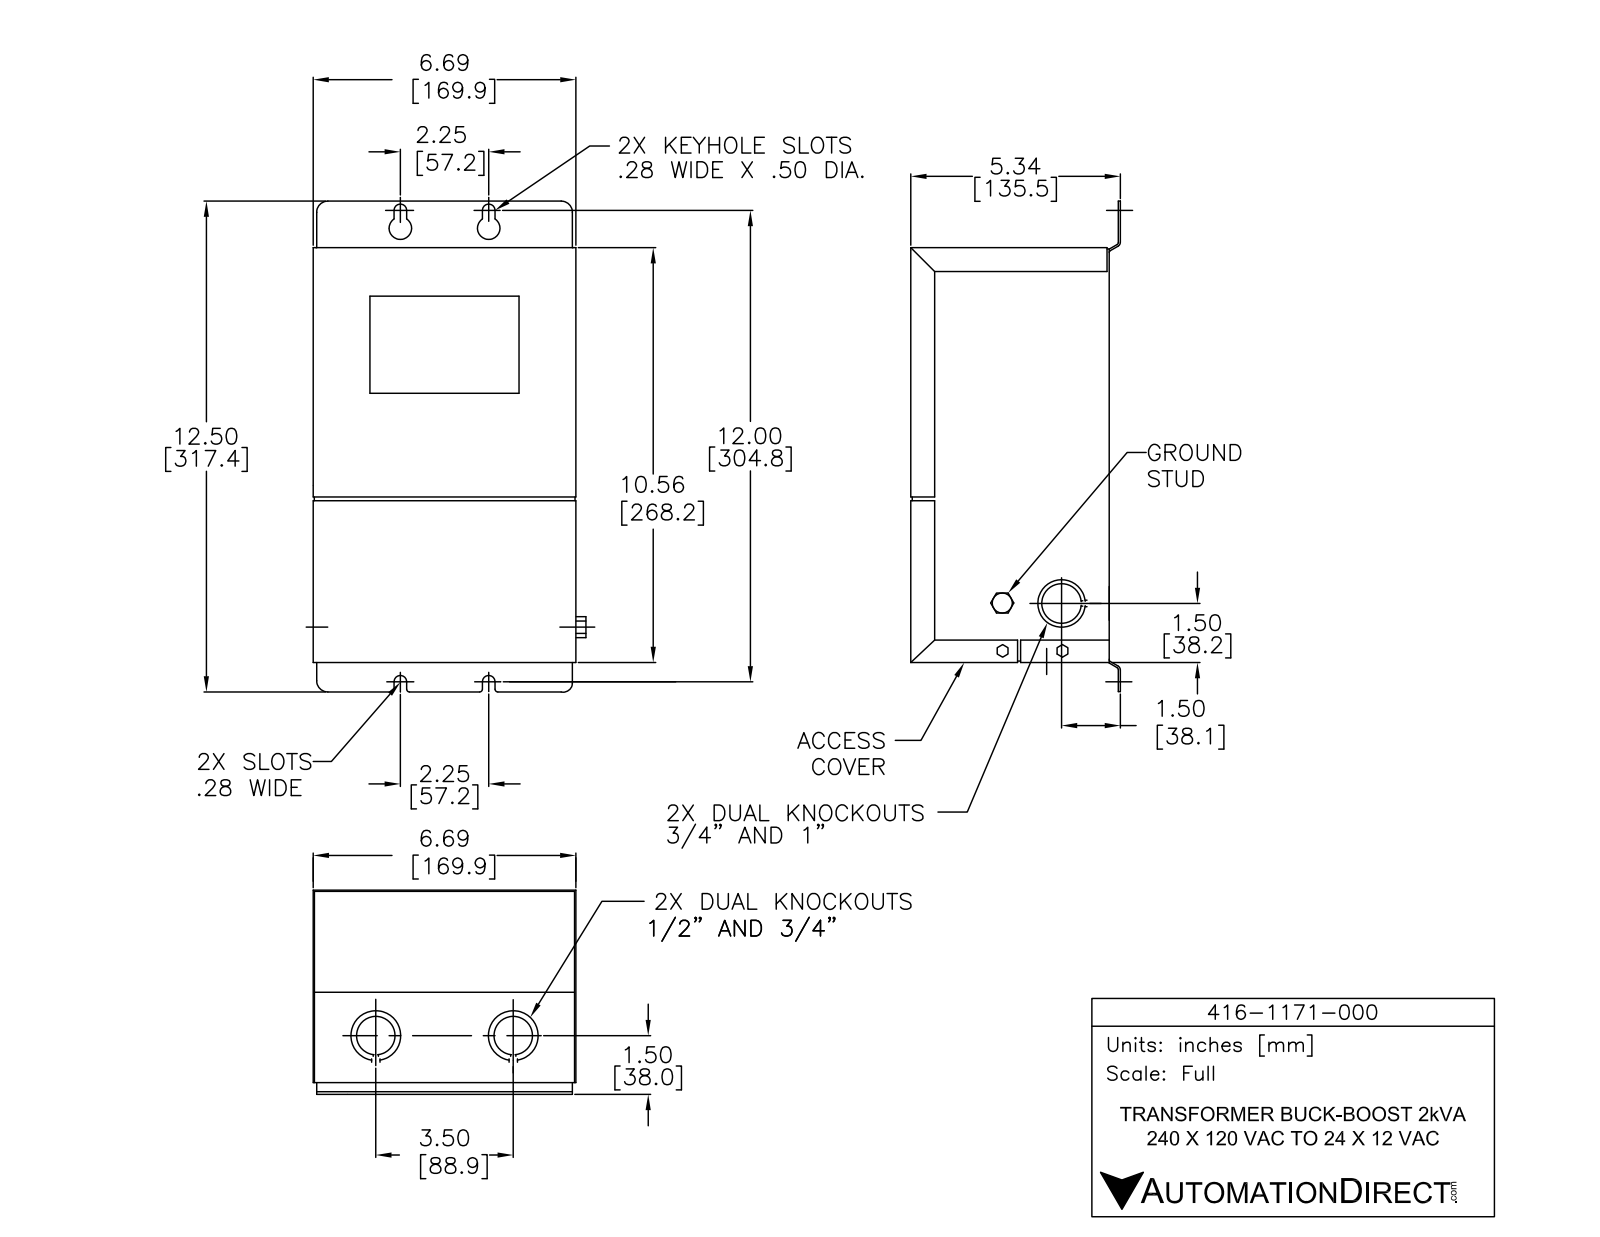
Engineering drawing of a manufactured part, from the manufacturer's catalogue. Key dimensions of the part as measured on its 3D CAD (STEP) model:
Part name (STEP PRODUCT): 416-1171-000
STEP written by: SolidWorks 2013 (AUTOMOTIVE_DESIGN)
Units: inches
Bodies: 1 solid, 186 faces (114 planar, 64 cylindrical, 8 other)
Overall size (bounding box): 12.5 × 6.9 × 5.341
Volume: 362.1 in³ · Surface area: 348.2 in²
Round holes (diameter × count): ⌀0.5 ×2, ⌀0.875 ×2, ⌀0.24 ×1, ⌀0.29 ×1, ⌀0.875 ×1
Round bosses / shafts (diameter × count): ⌀1.11 ×2, ⌀1.125 ×1
Partial cylindrical surfaces — rounded edges, fillets, slot ends (radius × count): R0.04 ×10, R0.25 ×10, R0.14 ×5, R0.08 ×2, R0.1 ×1, R0.167 ×1, R0.207 ×1
Main face-to-face distances: 5.12, 6.62, 0.04, 10.64, 6.66, 5.121, 6.7, 5.3, 0.18, 5.301
Hole centre spacings: 1.361, 1.371, 2.25, 2.35, 3.5
